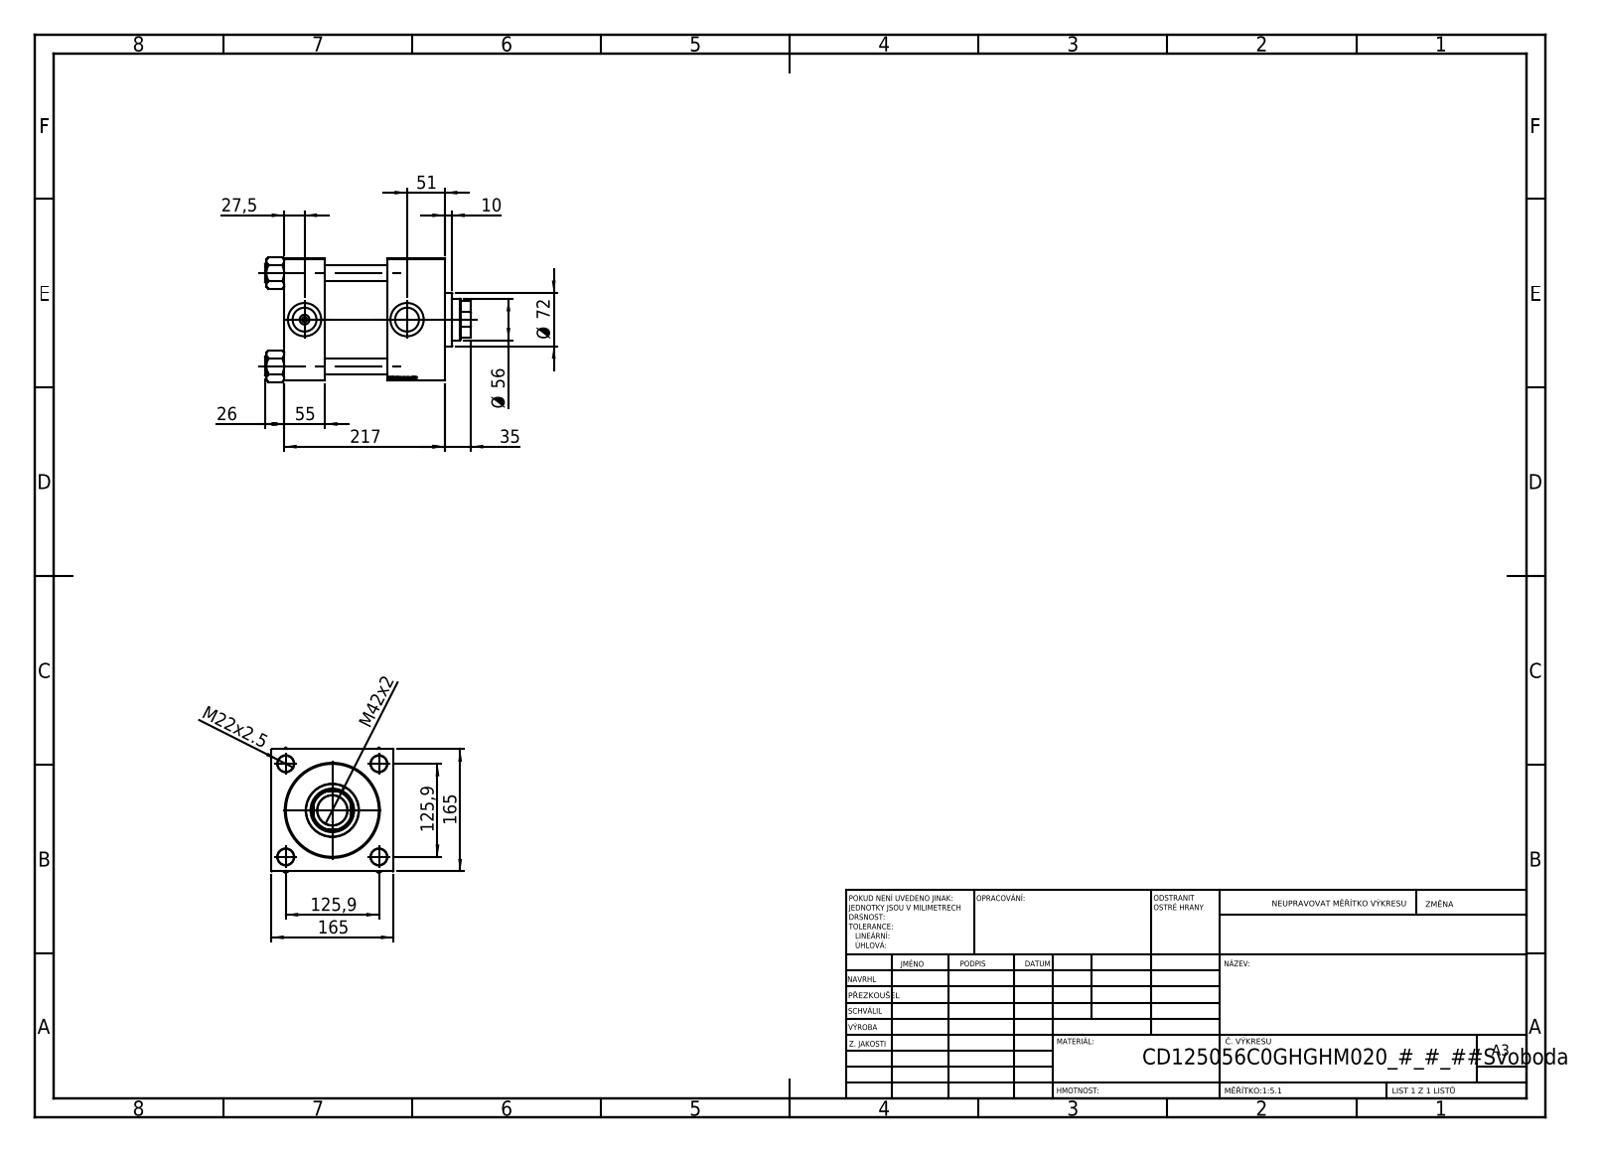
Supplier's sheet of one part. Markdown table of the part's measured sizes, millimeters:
| quantity | value |
| --- | --- |
| part name | V215CD_VC_C; V215CD_C_TYCINKA; V215CD_VCP_C; NUT_M5_V215CD_C (+1 more) |
| STEP written by | SolidWorks 2019 (CONFIG_CONTROL_DESIGN) |
| units | millimeters |
| bodies | 11 solids, 1196 faces (574 planar, 86 cylindrical, 536 other) |
| overall size | 278 × 169.14 × 165 |
| volume | 4 494 000 mm³ |
| surface area | 503 770 mm² |
| round holes (diameter × count) | 22 × 4, 7 × 2, 32.24 × 2, 45 × 2, 40.5 × 1, 56 × 1, 59 × 1, 96 × 1, 125 × 1, 125.5 × 1 |
| round bosses / shafts (diameter × count) | 25 × 4, 131 × 1, 72 × 1 |
| partial cylindrical surfaces (radius × count) | 27 × 1 |
| main face-to-face distances | 165, 55, 162, 217, 139, 84, 78, 188.3, 133.3, 49.3 |
| hole center spacings | 89.02, 125.9, 178.05, 138.5 |
